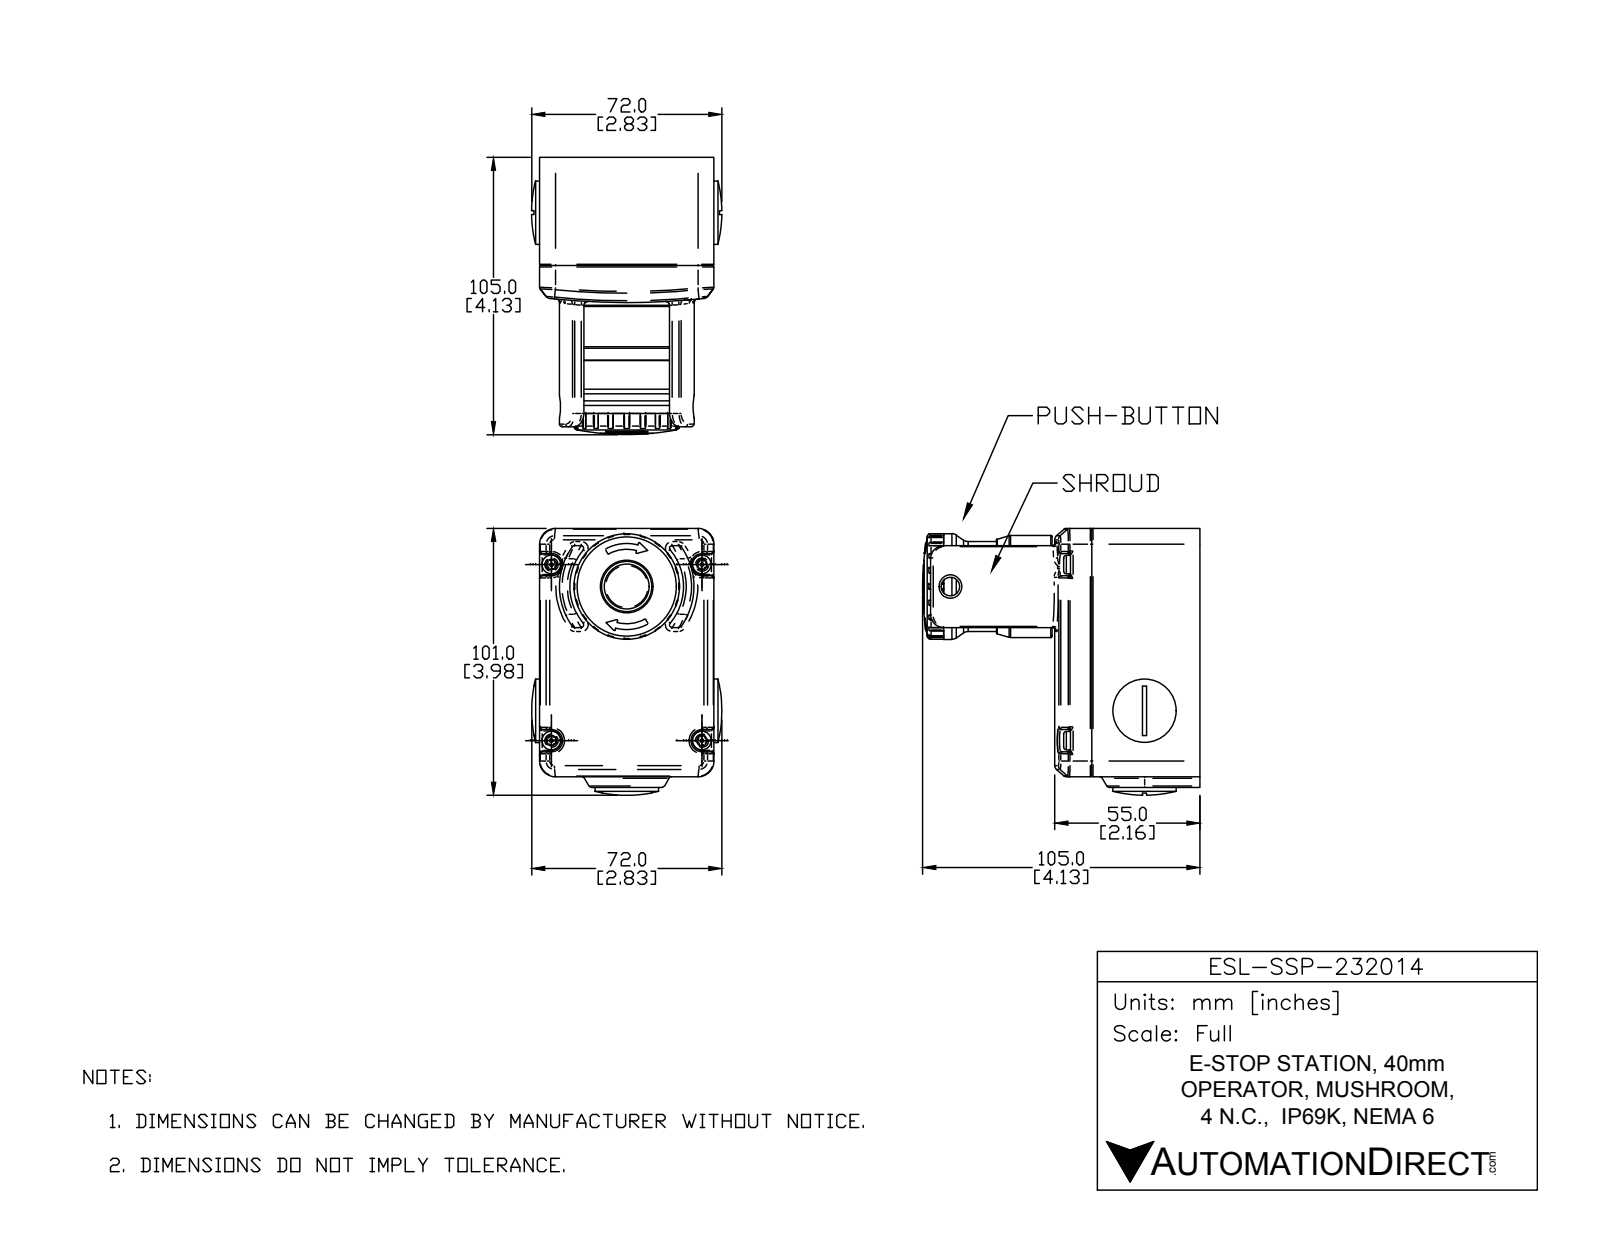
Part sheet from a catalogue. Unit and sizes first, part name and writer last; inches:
Units: inches
Overall size (bounding box): 4.134 × 3.976 × 2.834
Round holes (diameter × count): ⌀0.177 ×4, ⌀0.276 ×1, ⌀1.224 ×1, ⌀1.457 ×1
Round bosses / shafts (diameter × count): ⌀0.276 ×4, ⌀0.039 ×4, ⌀0.945 ×2, ⌀1.575 ×1, ⌀1.52 ×1, ⌀1.339 ×1
Partial cylindrical surfaces — rounded edges, fillets, slot ends (radius × count): R0.004 ×80, R0.03 ×24, R0.02 ×14, R0.039 ×13, R0.059 ×6, R0.008 ×4, R0.165 ×4, R0.236 ×4
Main face-to-face distances: 1.614, 2.598, 2.205, 0.591, 3.858, 0.157, 3.701, 2.236, 0.622, 0.031
Hole centre spacings: 1.235, 2.126, 2.807, 3.228, 3.865
Volume: 22.95 in³ · Surface area: 103.9 in²
Bodies: 11 solids, 776 faces (222 planar, 279 cylindrical, 275 other)
Part name (STEP PRODUCT): ESL-SSP-232014
STEP written by: SolidWorks 2016 (AUTOMOTIVE_DESIGN)
